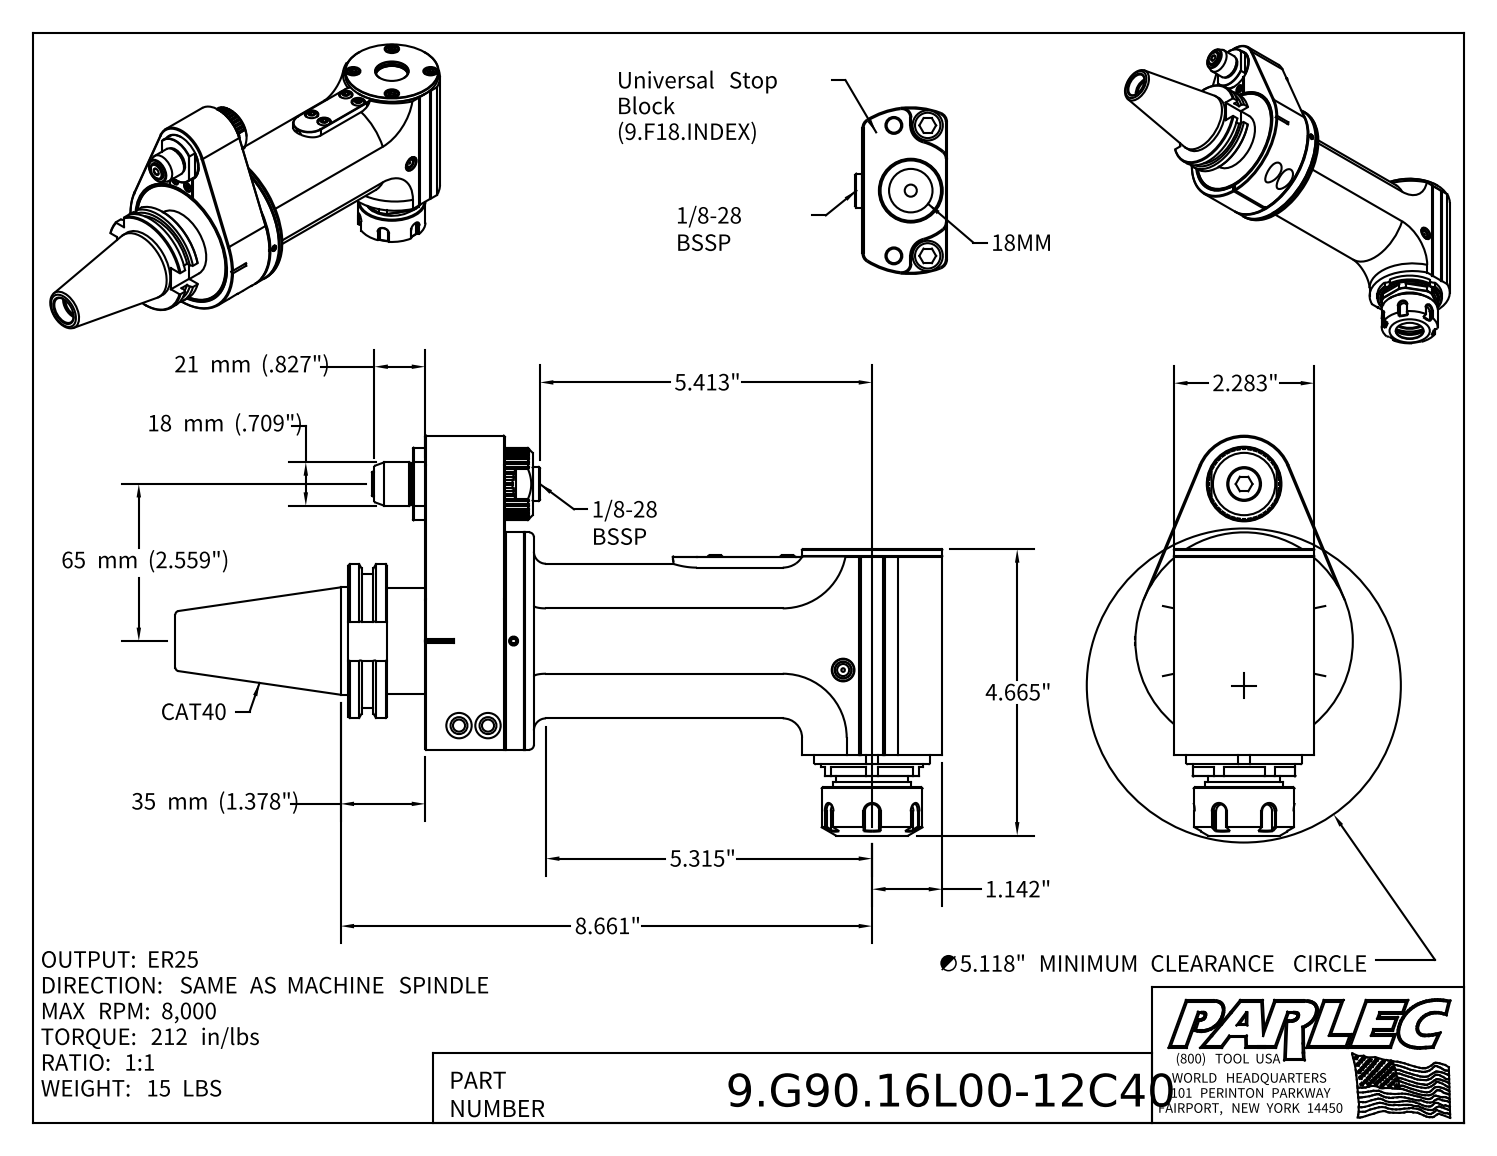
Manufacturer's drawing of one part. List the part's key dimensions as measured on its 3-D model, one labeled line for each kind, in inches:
Part name (STEP PRODUCT): 9.G90.16L00-12C40; 9_G90_16L00; 9_GA1_146_1 (Classic, Type 1, Cat40, 65mm)
STEP written by: Autodesk Inventor 2022 (AUTOMOTIVE_DESIGN)
Units: inches
Bodies: 4 solids, 1193 faces (751 planar, 197 cylindrical, 245 other)
Overall size (bounding box): 12.496 × 6.516 × 3.543
Volume: 65.78 in³ · Surface area: 234.2 in²
Round holes (diameter × count): ⌀0.165 ×6, ⌀0.118 ×4, ⌀0.13 ×4, ⌀0.197 ×4, ⌀0.315 ×4, ⌀0.157 ×2, ⌀0.236 ×2, ⌀0.276 ×2, ⌀0.335 ×2, ⌀0.413 ×2, ⌀0.551 ×2, ⌀0.354 ×1
Round bosses / shafts (diameter × count): ⌀0.295 ×4, ⌀1.181 ×2, ⌀0.394 ×2, ⌀3.543 ×1, ⌀3.071 ×1, ⌀2.283 ×1, ⌀2.187 ×1, ⌀1.89 ×1
Partial cylindrical surfaces — rounded edges, fillets, slot ends (radius × count): R0.118 ×8, R1.26 ×3, R0.085 ×2, R0.197 ×2, R0.394 ×2, R0.079 ×1, R0.092 ×1, R0.098 ×1
Main face-to-face distances: 1.299, 0.315, 0.118, 0.984, 0.197, 2.283, 1.181, 0.626, 0.472, 0.157
Hole centre spacings: 1.476, 2.557, 0.366, 0.433, 0.551, 0.764, 0.78, 1.476
